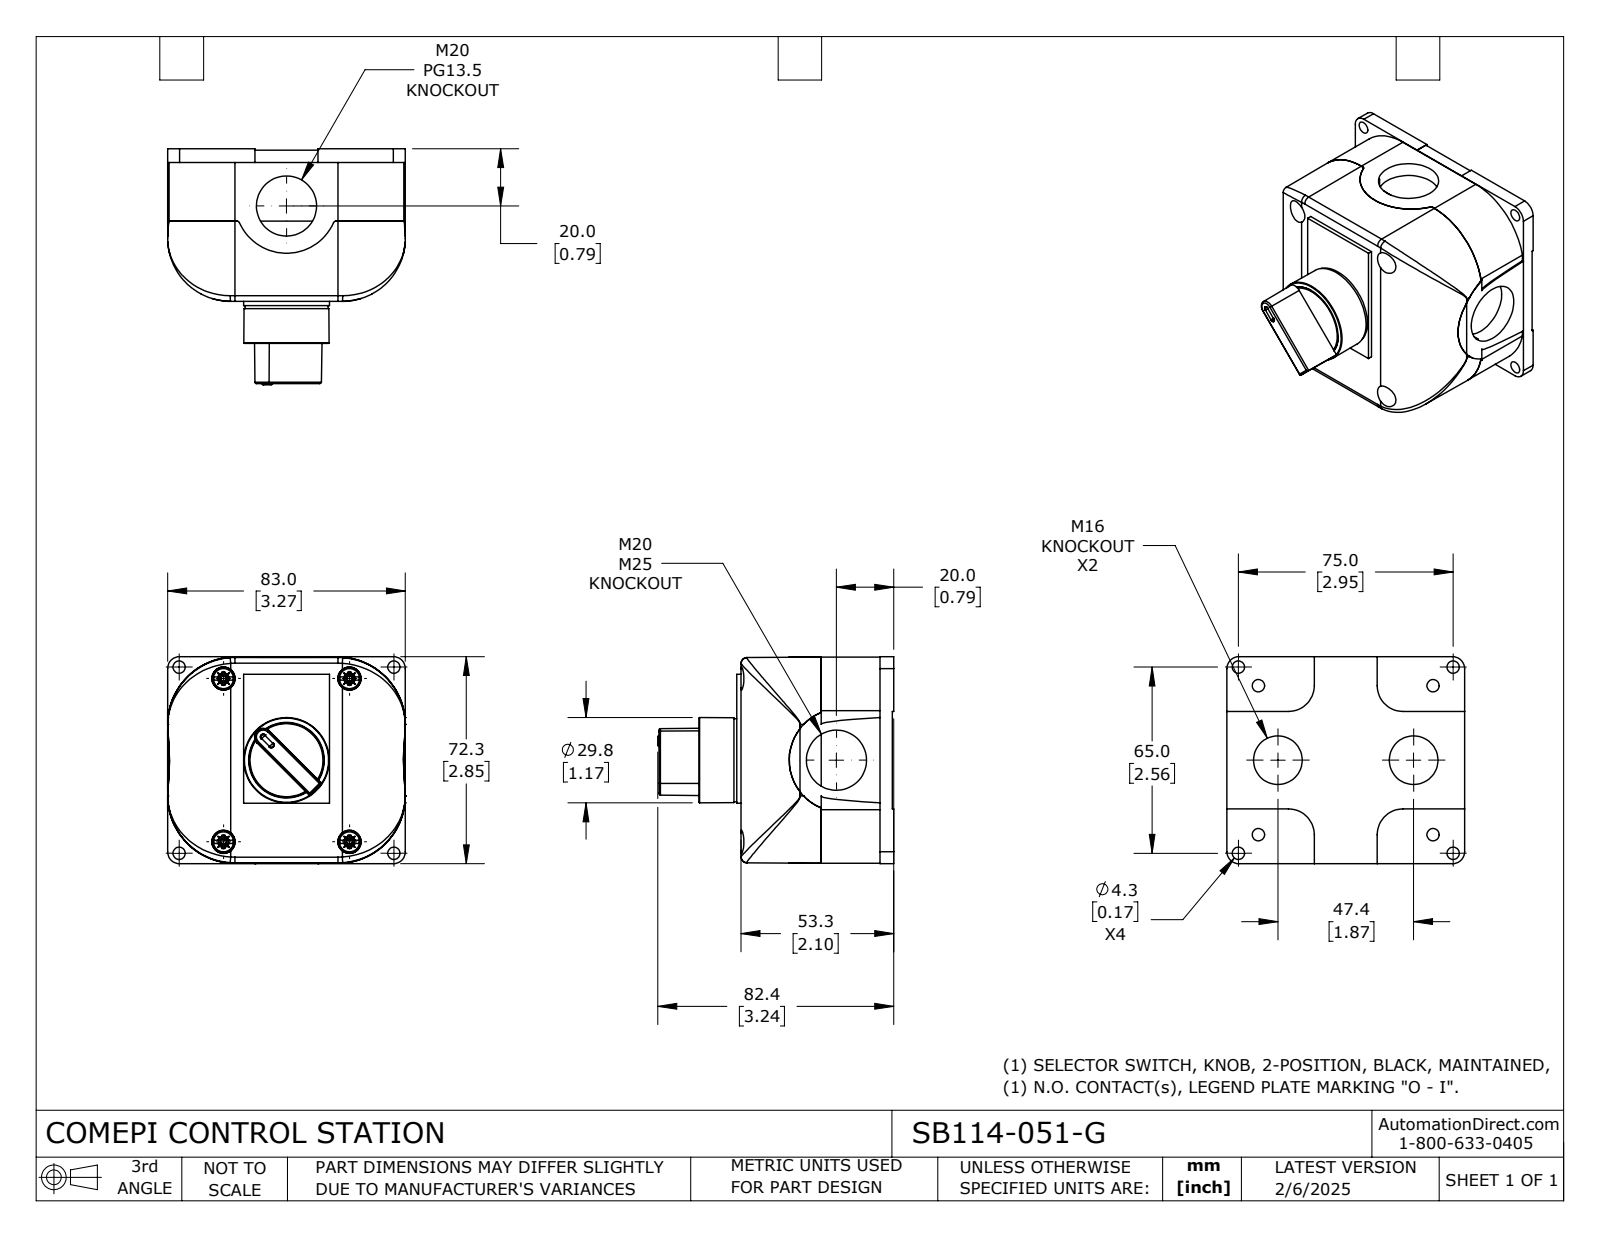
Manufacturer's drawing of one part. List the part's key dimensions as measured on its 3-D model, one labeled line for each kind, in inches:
Part name (STEP PRODUCT): SB114-051-G
STEP written by: SolidWorks 2024 (CONFIG_CONTROL_DESIGN)
Units: inches
Bodies: 5 solids, 586 faces (332 planar, 159 cylindrical, 95 other)
Overall size (bounding box): 3.268 × 3.244 × 2.846
Volume: 13.1 in³ · Surface area: 94.77 in²
Round holes (diameter × count): ⌀0.169 ×8, ⌀0.323 ×4, ⌀0.669 ×2, ⌀0.827 ×2, ⌀0.098 ×1, ⌀0.5 ×1, ⌀0.551 ×1, ⌀0.75 ×1, ⌀0.854 ×1, ⌀0.886 ×1, ⌀0.976 ×1, ⌀1.024 ×1
Round bosses / shafts (diameter × count): ⌀0.276 ×4, ⌀1.142 ×1, ⌀1.004 ×1, ⌀0.965 ×1, ⌀0.85 ×1, ⌀0.669 ×1, ⌀0.441 ×1, ⌀0.343 ×1
Partial cylindrical surfaces — rounded edges, fillets, slot ends (radius × count): R0.039 ×5, R0.035 ×4, R0.079 ×4, R0.354 ×4, R0.38 ×4, R0.925 ×4, R0.02 ×3, R0.01 ×2
Main face-to-face distances: 2.079, 0.098, 0.976, 1.102, 0.878, 1.98, 0.118, 0.02, 0.996, 2.098
Hole centre spacings: 0.376, 1.058, 1.39, 1.578, 1.954, 2.32, 2.367, 2.689
